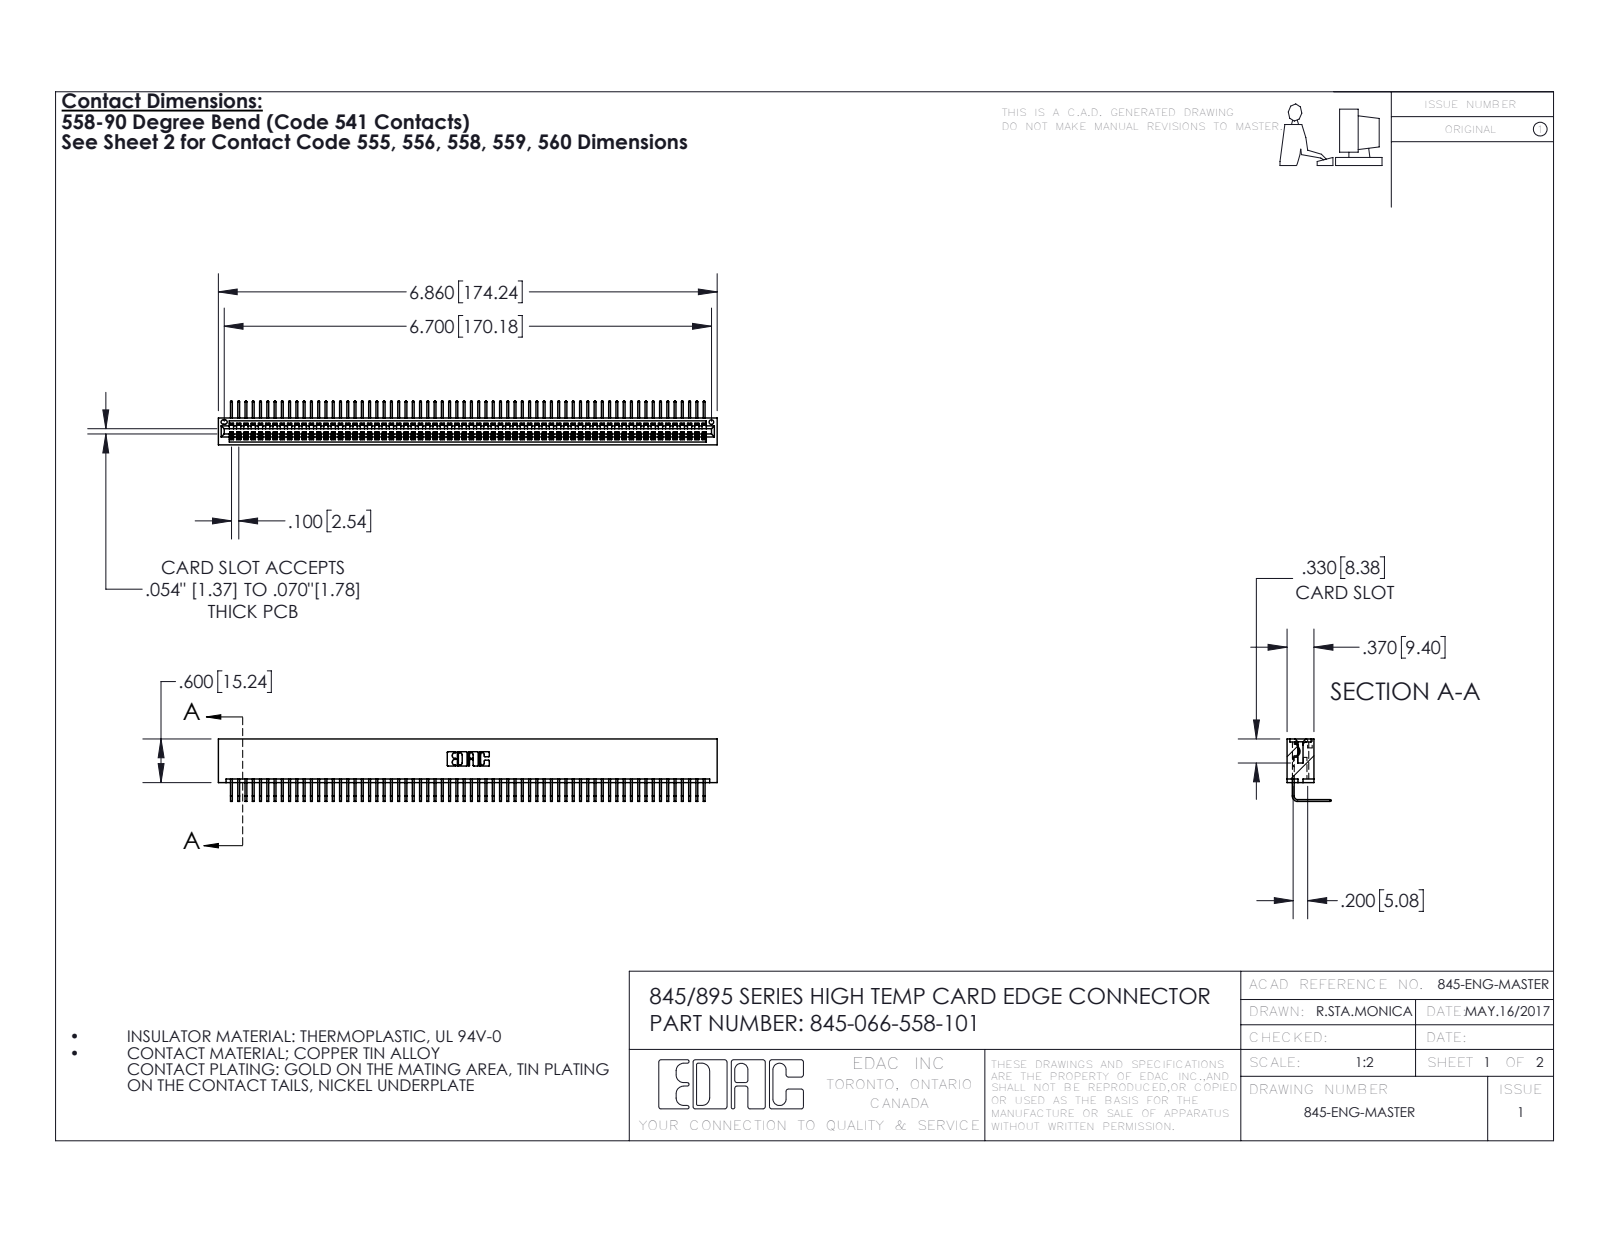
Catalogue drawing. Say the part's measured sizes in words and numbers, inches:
The part is named "345 Part_No Mounting Lugs; 345-066-558-101; 345-292-001_558 Tail - 2". Its 3-D file was written by "SolidWorks 2016 (CONFIG_CONTROL_DESIGN)". It is 67 solids with 4078 faces: 2848 planar, 1230 cylindrical and 0 other. Overall it measures 6.86 by 0.859 by 0.605 inches. Its volume is 1.071 cubic inches and its surface area 38.95 square inches. Round holes: 1 of diameter 0.064. Partial cylindrical surfaces (rounded edges, fillets, slot ends): 132 of radius 0.006, 22 of radius 0.01, 6 of radius 0.007, 6 of radius 0.031, 3 of radius 0.026, 2 of radius 0.031, 2 of radius 0.04, 1 of radius 0.014. The main face-to-face distances are 0.298, 0.072, 0.37, 0.2, 0.098, 0.272, 0.025, 0.225, 0.149, 0.072.
